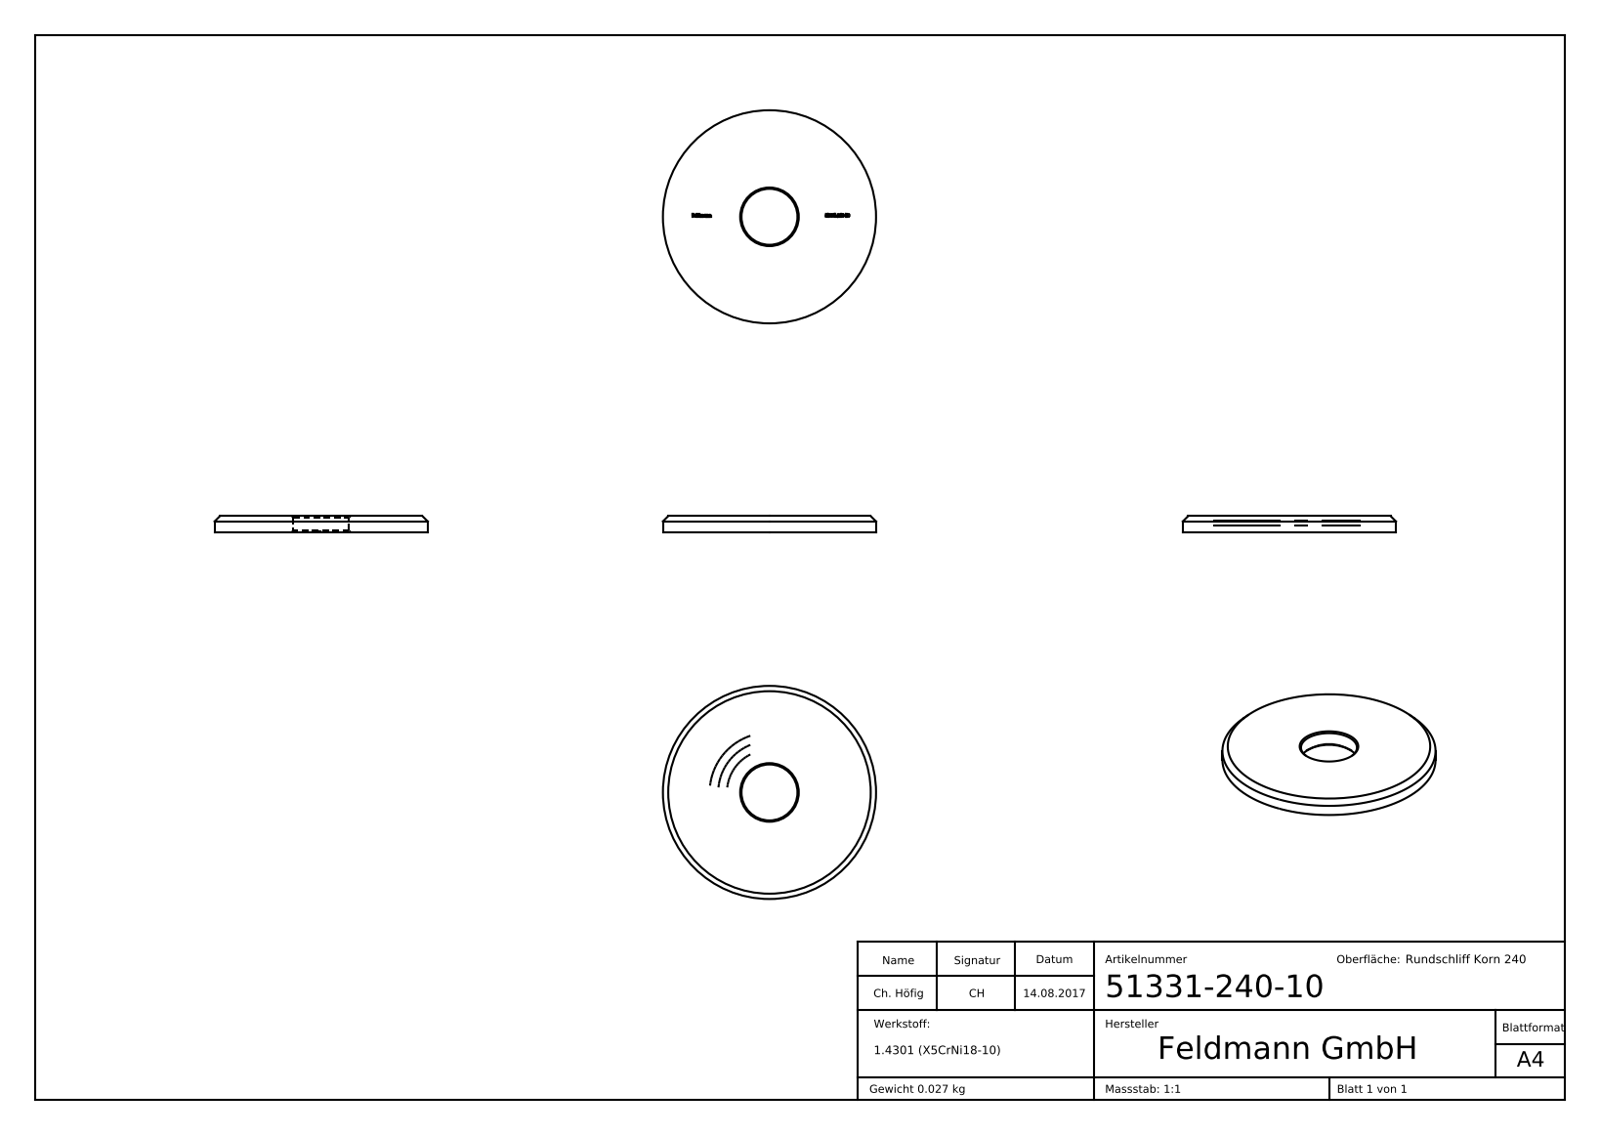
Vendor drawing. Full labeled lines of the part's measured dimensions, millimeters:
Part name (STEP PRODUCT): 51331-240-10
STEP written by: SolidWorks 2018 (CONFIG_CONTROL_DESIGN)
Units: millimetres
Bodies: 1 solid, 257 faces (139 planar, 4 cylindrical, 114 other)
Overall size (bounding box): 40 × 40 × 3
Volume: 3 446 mm³ · Surface area: 2 736 mm²
Round holes (diameter × count): ⌀10.5 ×1
Round bosses / shafts (diameter × count): ⌀40 ×1
Main face-to-face distances: 3, 2.9, 0.35, 25.94, 28.06, 24.72, 1.22, 3.34, 2.12, 1.19
